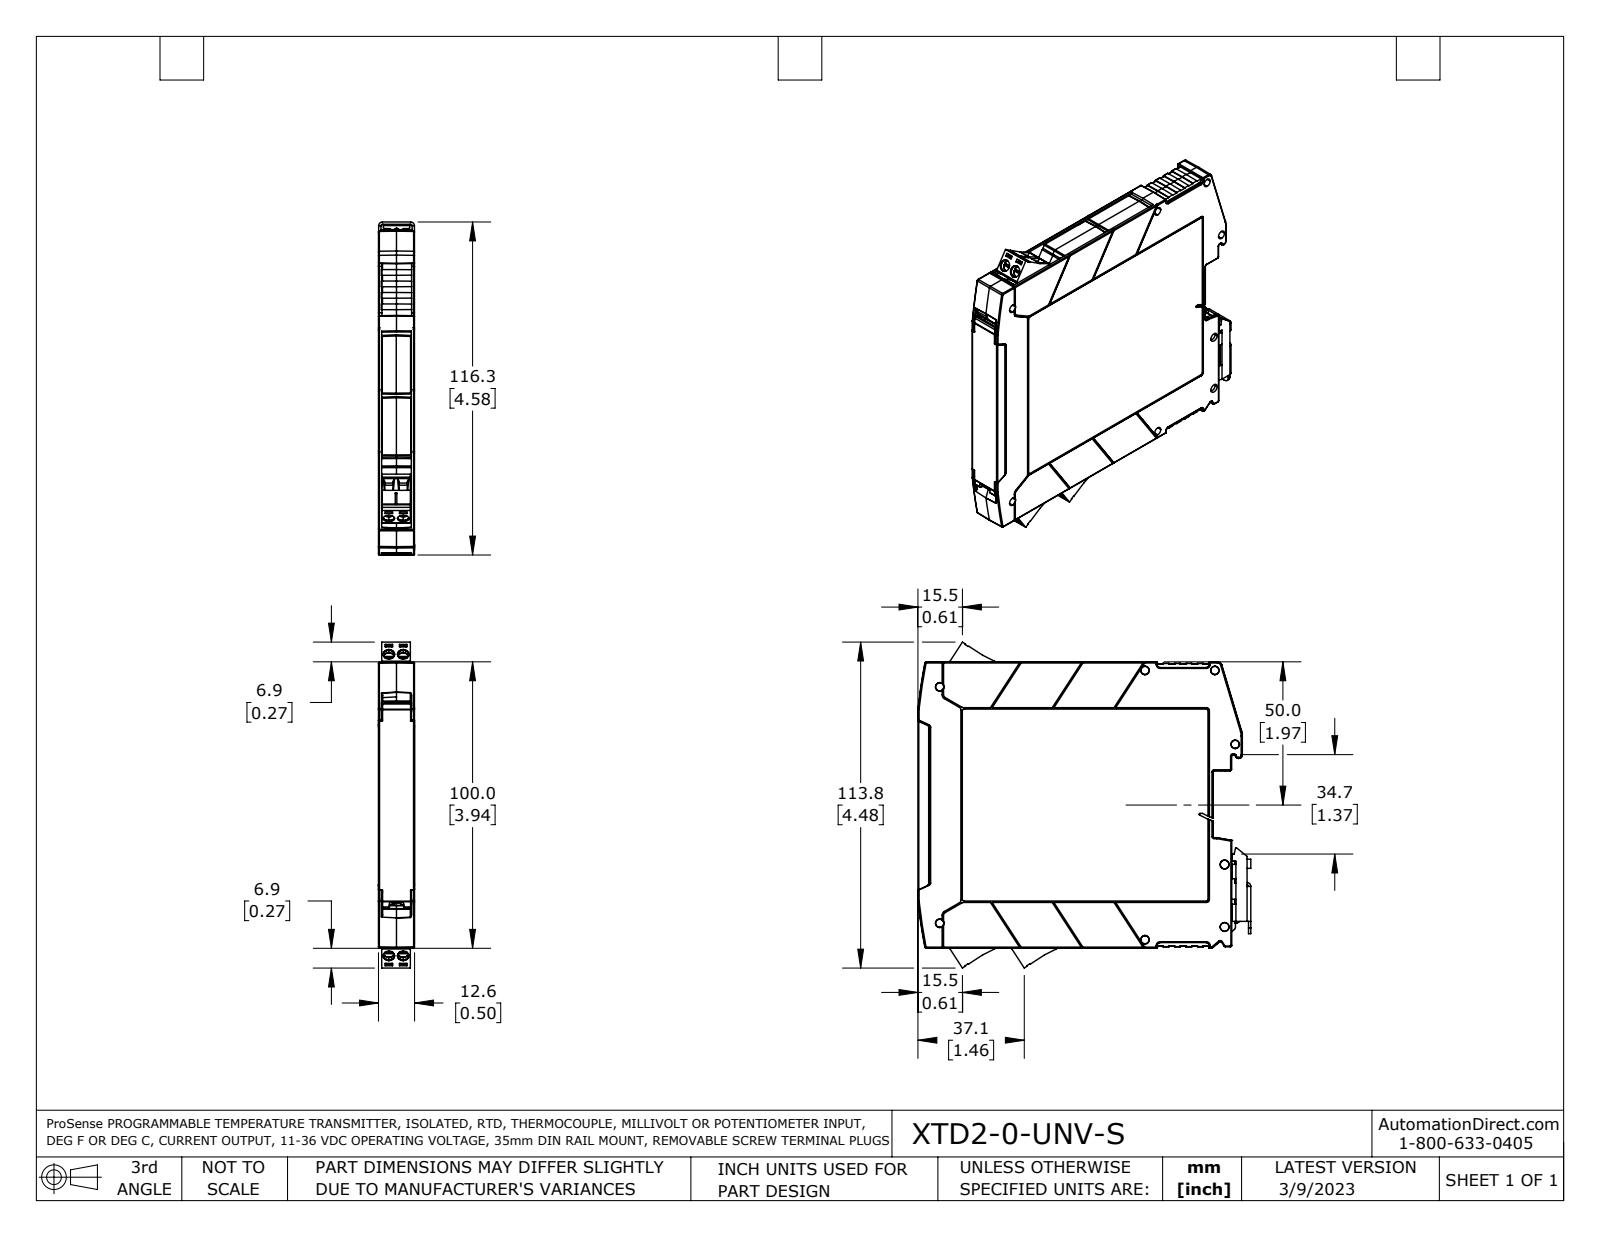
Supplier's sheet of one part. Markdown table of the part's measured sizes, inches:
| quantity | value |
| --- | --- |
| part name | XTD2-0-UNV-S |
| STEP written by | SolidWorks 2021 (AUTOMOTIVE_DESIGN) |
| units | inches |
| bodies | 1 solid, 3721 faces (2225 planar, 691 cylindrical, 805 other) |
| overall size | 4.577 × 4.48 × 0.496 |
| volume | 2.895 in³ |
| surface area | 99.38 in² |
| round holes (diameter × count) | 0.11 × 6, 0.152 × 6, 0.159 × 6, 0.175 × 1 |
| round bosses / shafts (diameter × count) | 0.156 × 6, 0.098 × 6, 0.055 × 6, 0.059 × 2, 0.053 × 2 |
| partial cylindrical surfaces (radius × count) | 0.008 × 92, 0.012 × 77, 0.02 × 77, 0.009 × 24, 0.039 × 22, 0.004 × 20, 0.016 × 13, 0.006 × 12 |
| main face-to-face distances | 0.049, 0.445, 0.494, 0.396, 0.043, 0.451, 0.402, 0.031, 0.047, 0.203 |
| hole center spacings | 0.197, 0.463, 0.503 |
